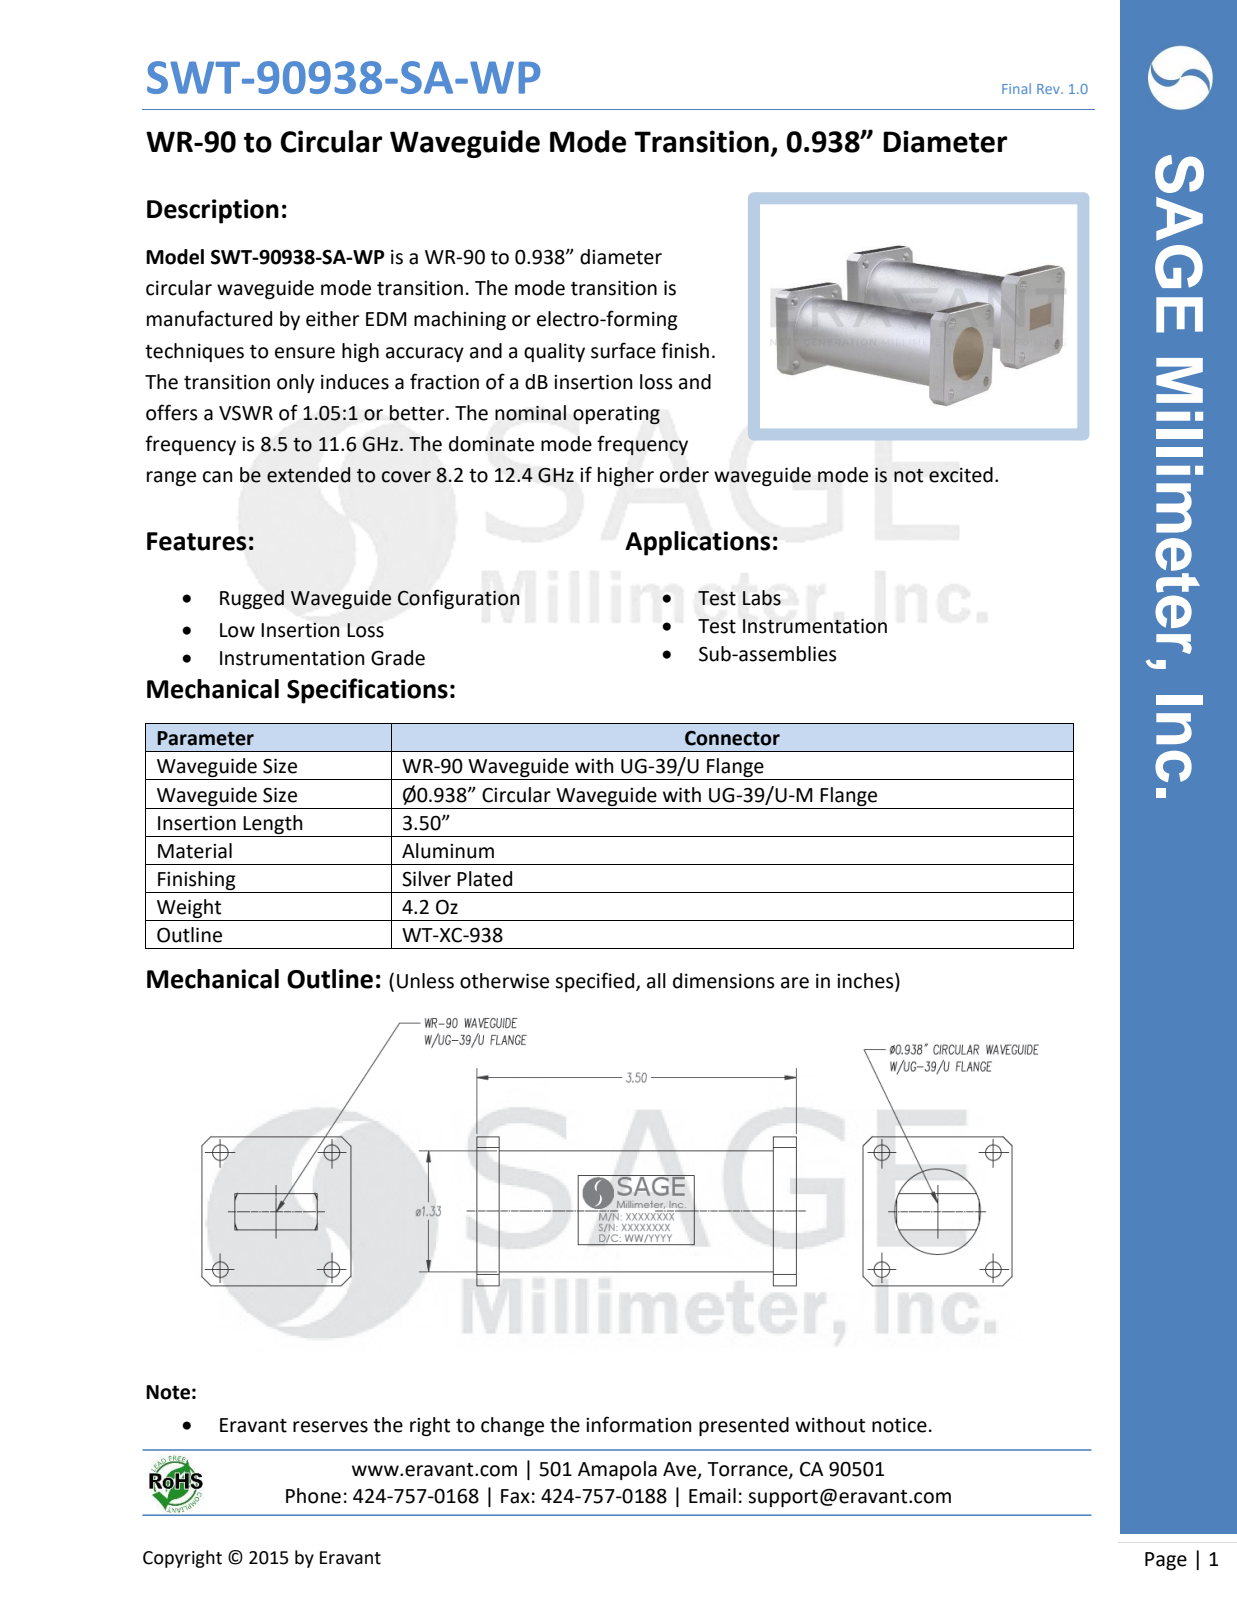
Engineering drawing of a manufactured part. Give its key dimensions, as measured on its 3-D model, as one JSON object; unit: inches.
{"part_name": "SWT-90938-SA", "step_written_by": "SolidWorks 2016 (AUTOMOTIVE_DESIGN)", "units": "inches", "bodies": {"solids": 1, "faces": 78, "planar": 58, "cylindrical": 20, "other": 0}, "overall_size": [3.5, 1.63, 1.63], "volume_in3": 5.438, "surface_area_in2": 24.01, "round_holes": [[0.172, 4], [0.938, 1]], "round_bosses_or_shafts": [[1.33, 1]], "face_to_face_distances": [0.25, 3.25, 3.5, 1.63, 3, 3.499, 0.249, 3.249, 3.498, 2.164], "hole_center_spacings": [0.884, 1.22, 1.28, 1.768]}
